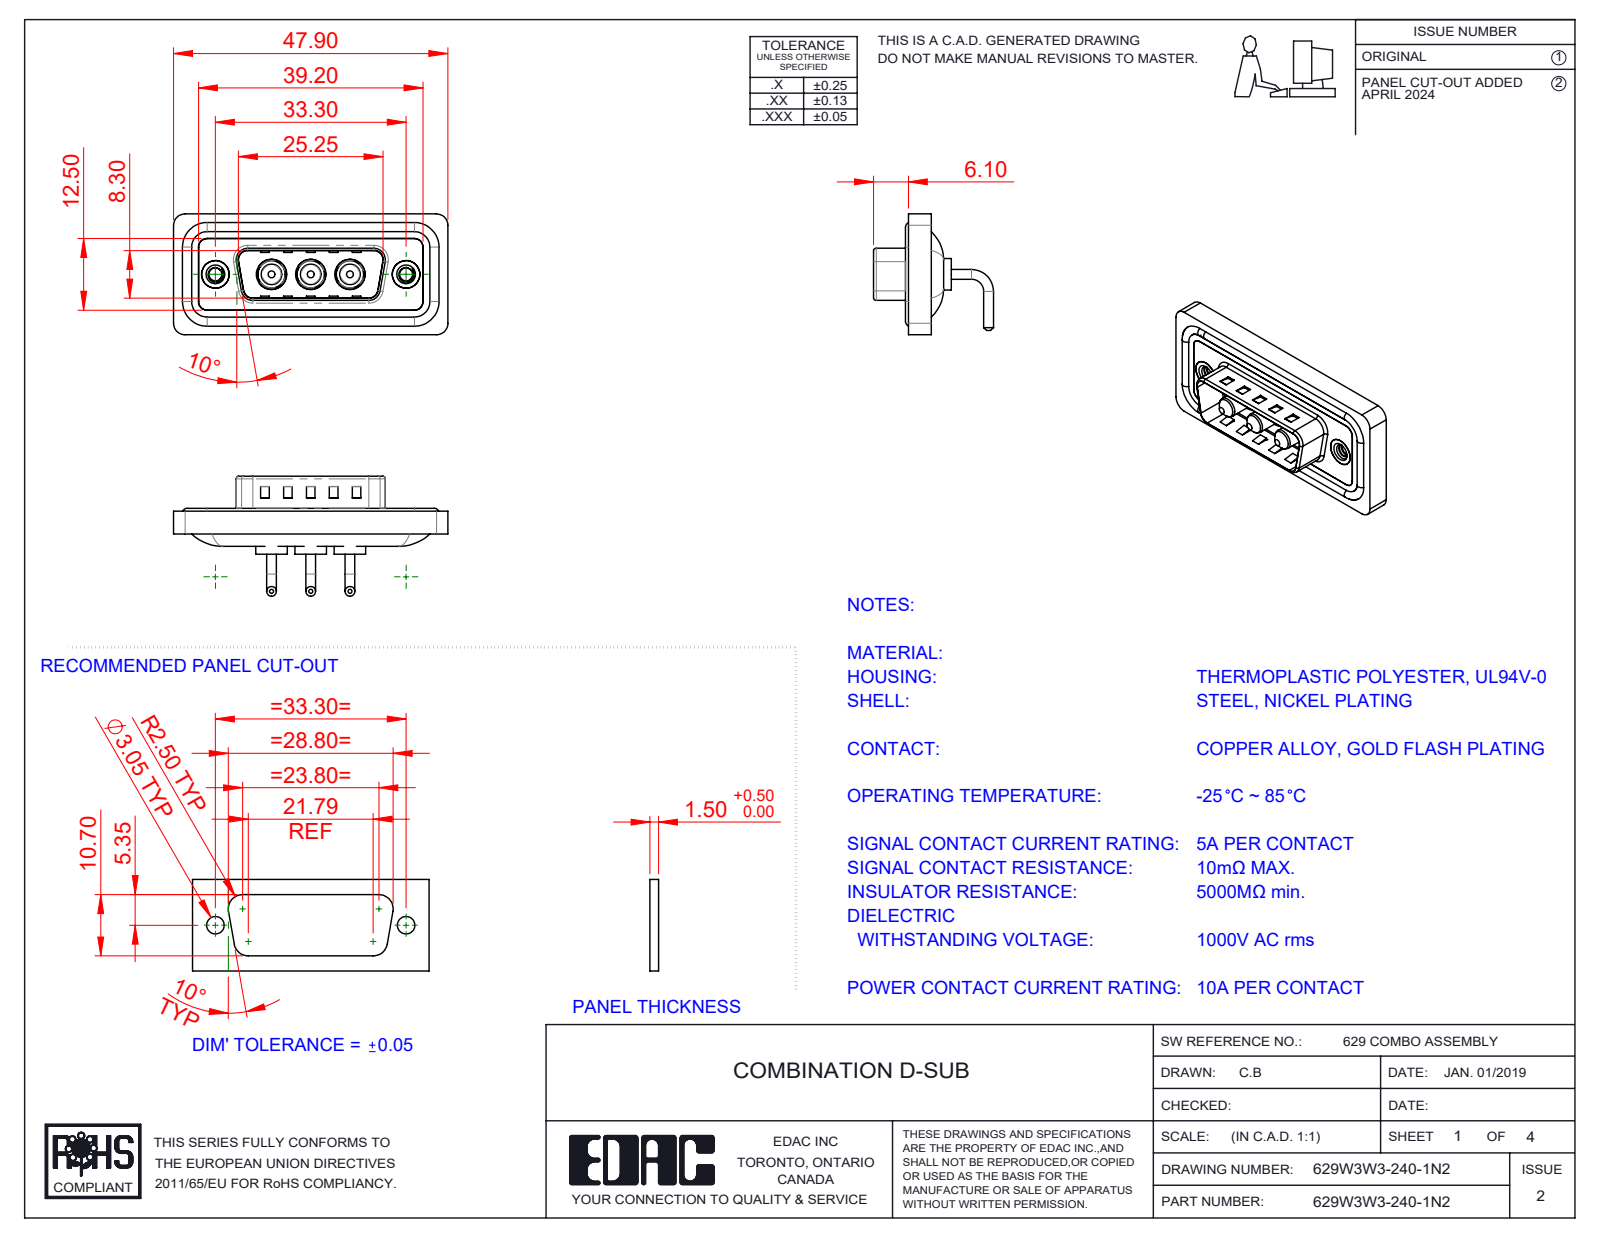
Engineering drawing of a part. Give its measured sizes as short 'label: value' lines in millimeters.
name: 629Combo Shell Rear_15 Contacts; 629Combo Threaded Rivet_2; 629W3W3-140-1N2; 629Combo Shell Front_15 Contacts (+3 more)
written by: SolidWorks 2023 (CONFIG_CONTROL_DESIGN)
unit: mm
bodies: 13 solids, 576 faces (207 planar, 247 cylindrical, 122 other)
size: 47.9 × 21.1 × 20.95
volume: 5 615 mm³; area: 8 884 mm²
holes: 3× ⌀4.85, 3× ⌀5.3, 2× ⌀2.26, 2× ⌀4, 2× ⌀4.8, 2× ⌀5
bosses: 6× ⌀1.7, 4× ⌀1.6, 3× ⌀5.5, 3× ⌀5.2, 3× ⌀4.75, 3× ⌀3.75, 3× ⌀3.6, 2× ⌀4.9
rounds: 20× R2, 18× R1.5, 8× R0.5, 8× R1.6, 4× R0.25, 4× R0.6, 4× R0.65, 4× R0.9
face distances: 0.4, 2.9, 0.8, 1.1, 2.1, 1.6, 3.1, 2.5, 4.5, 1.5
hole spacings: 6.85, 9.8, 16.65, 23.5, 13.7, 33.3
